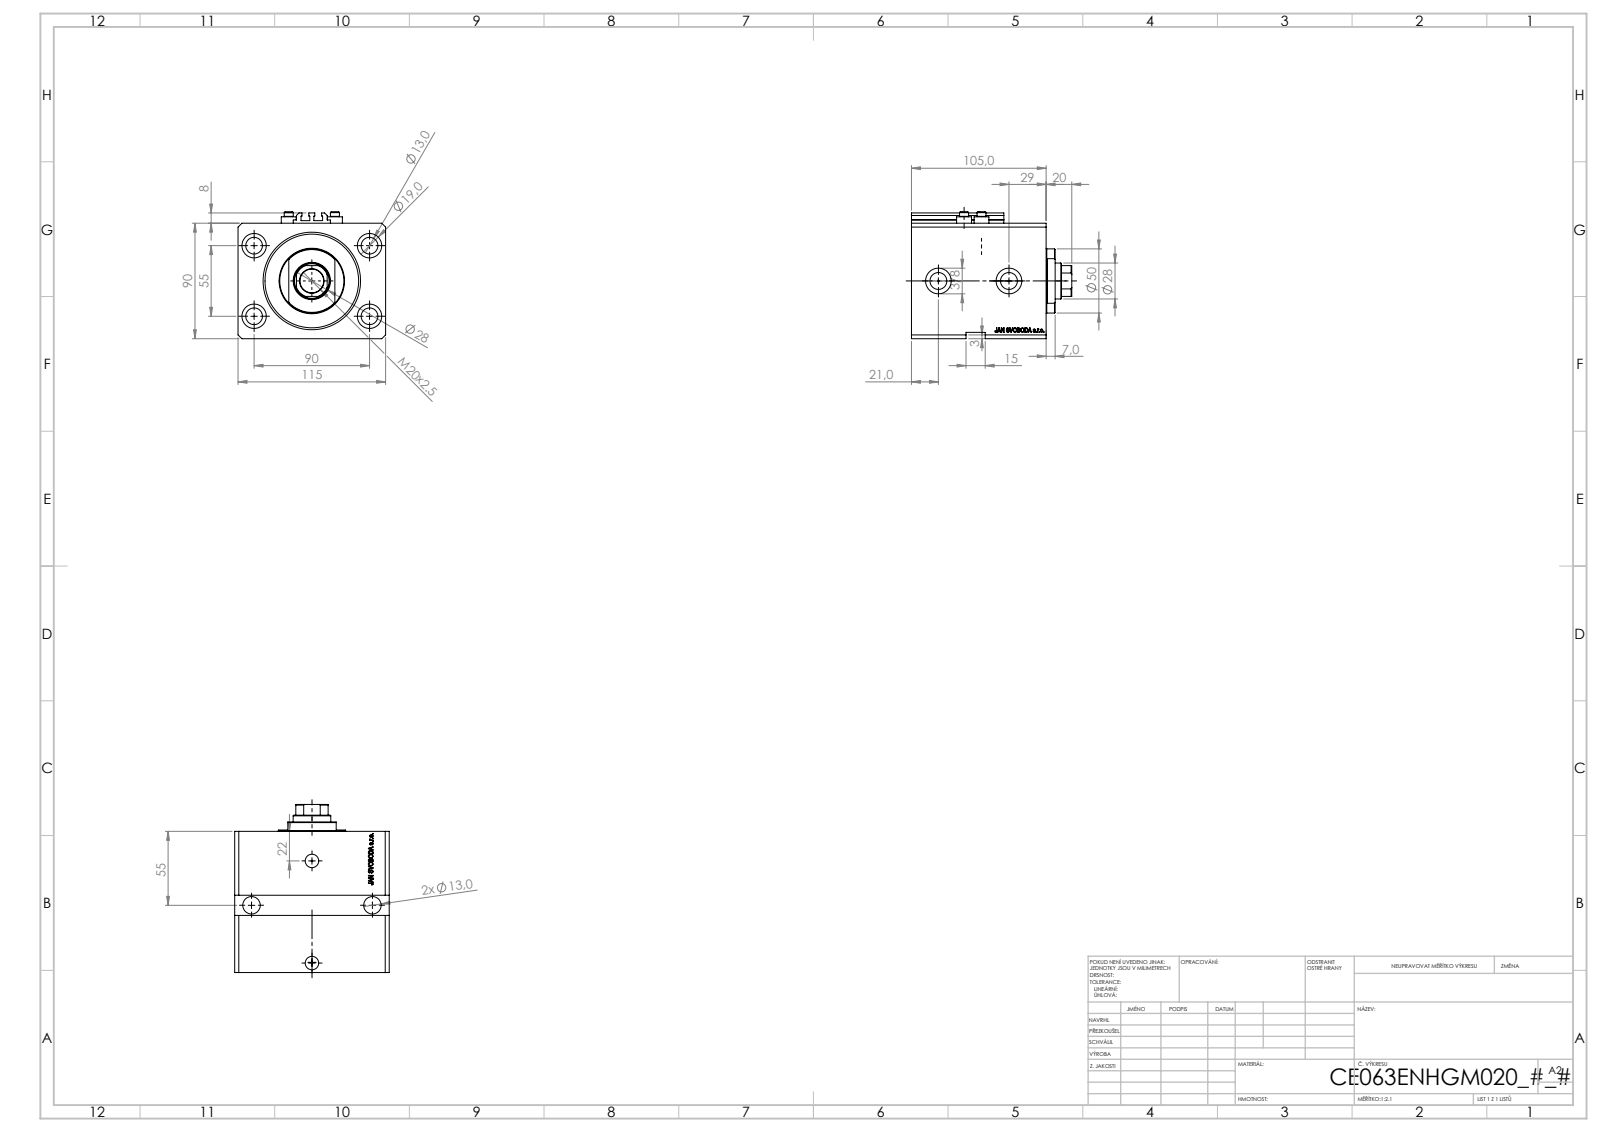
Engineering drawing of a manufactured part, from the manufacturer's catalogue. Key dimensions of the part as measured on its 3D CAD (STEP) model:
Part name (STEP PRODUCT): V250CE_VC_E; V250CE_E_Body; ALLEN BOLT V250CE; V250CE_C_VCP
STEP written by: SolidWorks 2019 (CONFIG_CONTROL_DESIGN)
Units: millimetres
Bodies: 8 solids, 1107 faces (543 planar, 126 cylindrical, 438 other)
Overall size (bounding box): 125 × 115 × 99
Volume: 954 568 mm³ · Surface area: 153 949 mm²
Round holes (diameter × count): ⌀13 ×6, ⌀1.25 ×4, ⌀4 ×4, ⌀19 ×4, ⌀10 ×2, ⌀13.16 ×2, ⌀20 ×2, ⌀18.5 ×1, ⌀28 ×1, ⌀63 ×1, ⌀76 ×1
Round bosses / shafts (diameter × count): ⌀11.6 ×4, ⌀7 ×4, ⌀50 ×1
Partial cylindrical surfaces — rounded edges, fillets, slot ends (radius × count): R0.2 ×10, R13.5 ×1
Main face-to-face distances: 90, 20, 115, 85, 105, 87.1, 17.9, 67.1, 40, 65
Hole centre spacings: 52.74, 55, 90, 13.6, 27.39, 28.46, 33.62, 36
